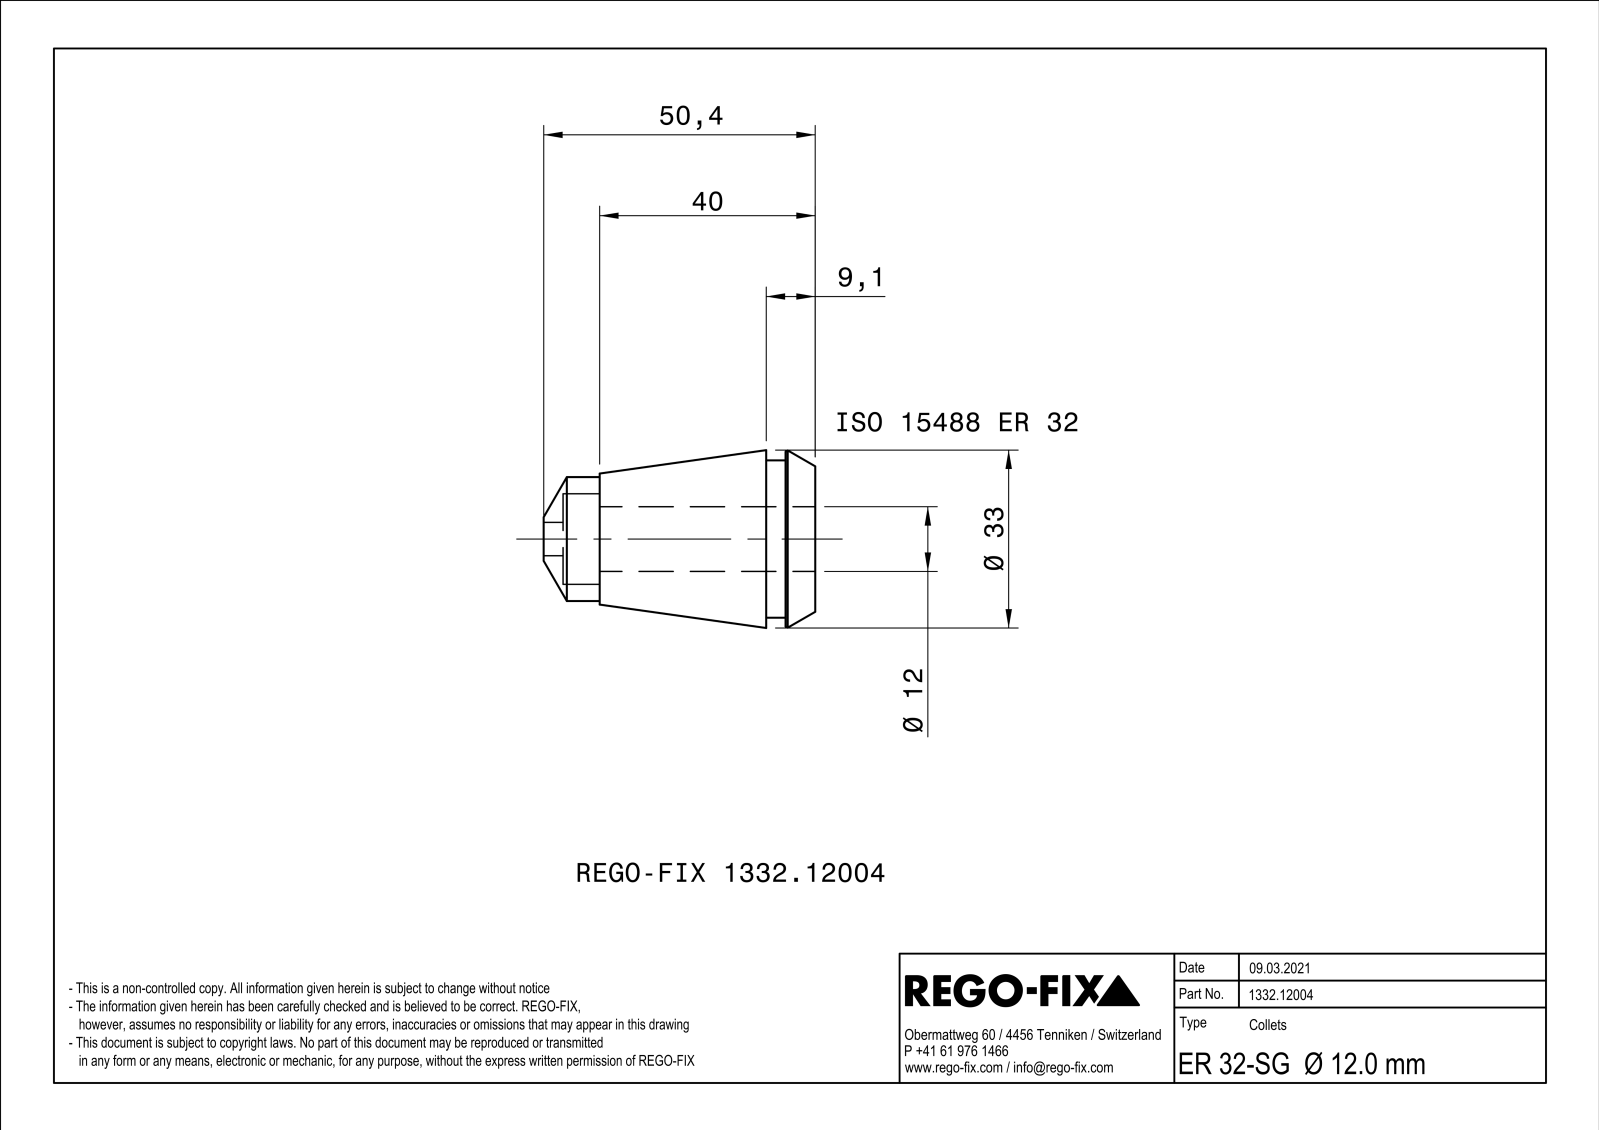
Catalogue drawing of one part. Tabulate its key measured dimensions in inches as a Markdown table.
| quantity | value |
| --- | --- |
| part name | NOCUT |
| STEP written by | SIEMENS PLM Software Solid Edge ST10 (AUTOMOTIVE_DESIGN) |
| units | inches |
| bodies | 1 solid, 245 faces (121 planar, 36 cylindrical, 88 other) |
| overall size | 2.205 × 1.299 × 1.299 |
| volume | 1.209 in³ |
| surface area | 24.01 in² |
| round holes (diameter × count) | 0.118 × 1, 0.472 × 1, 0.661 × 1, 0.748 × 1, 0.787 × 1, 0.874 × 1 |
| round bosses / shafts (diameter × count) | 1.15 × 1, 0.906 × 1, 0.78 × 1, 0.768 × 1, 0.74 × 1, 0.276 × 1, 0.173 × 1 |
| partial cylindrical surfaces (radius × count) | 0.122 × 1 |
| main face-to-face distances | 0.039, 0.079, 1.843, 1.575, 1.496, 0.346, 0.358, 1.138, 1.484, 0.142 |
